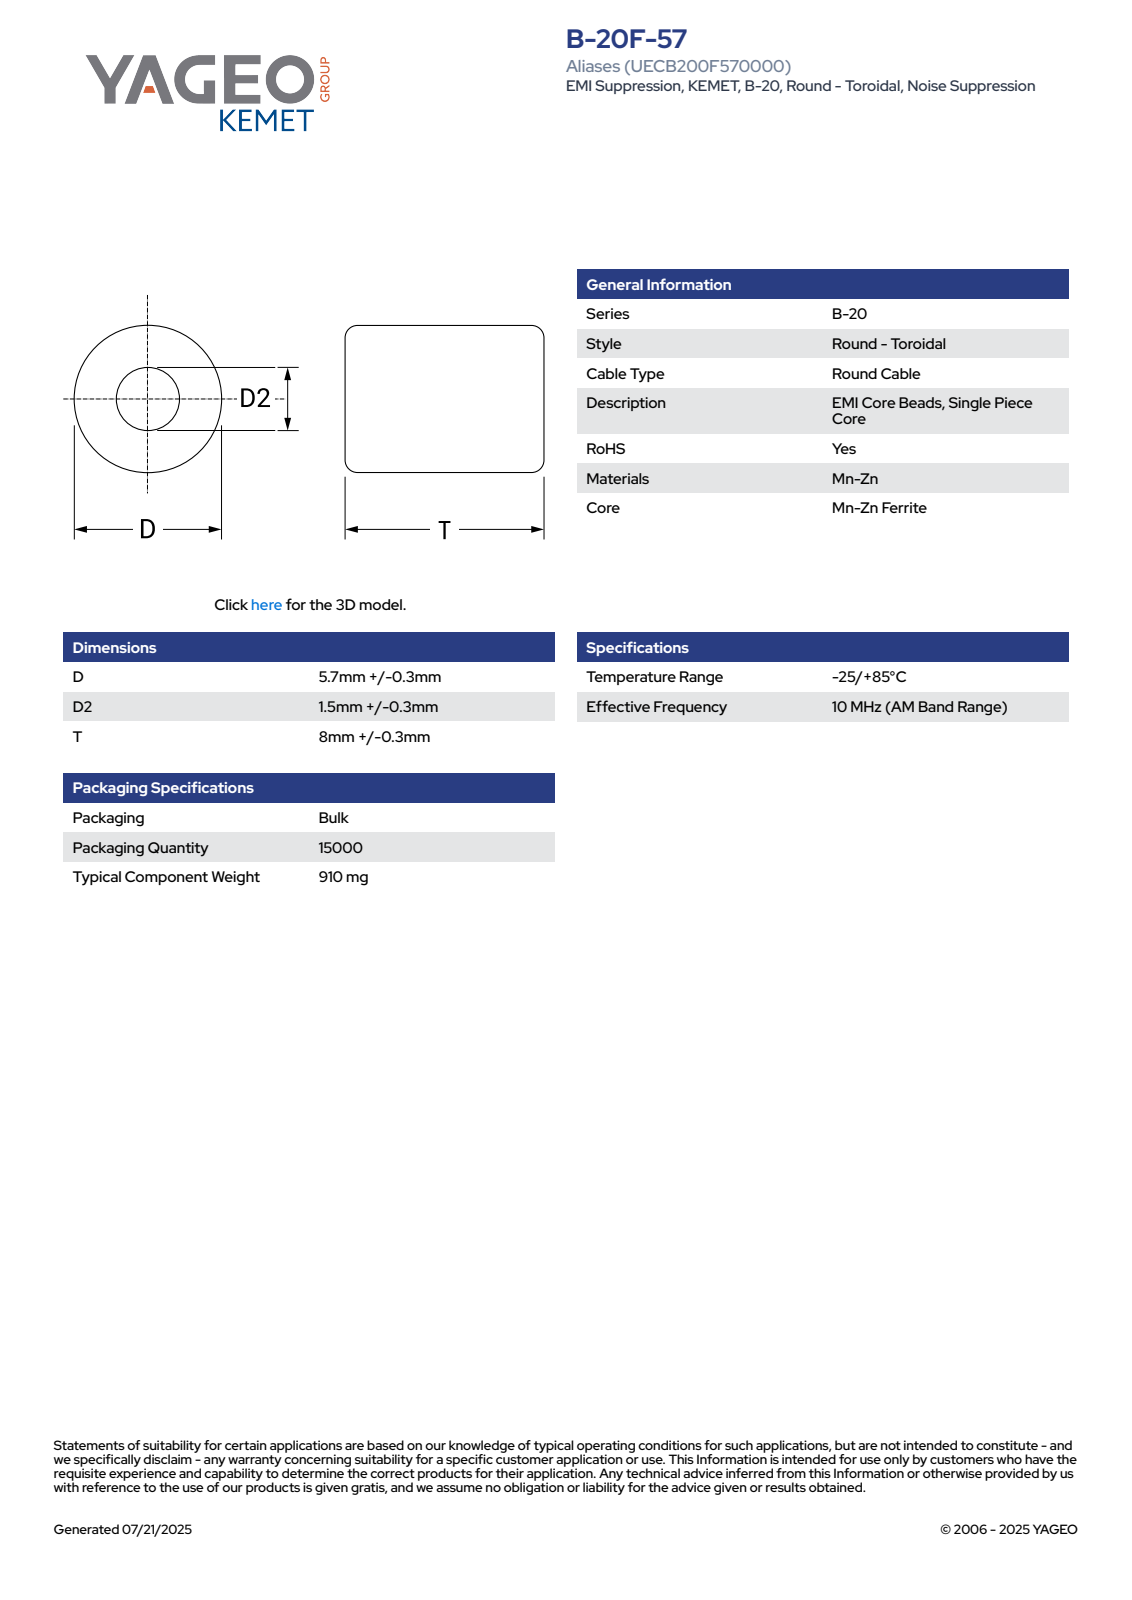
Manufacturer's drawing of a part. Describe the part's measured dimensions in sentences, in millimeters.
The part is named "EC_KBCH_D6D21.5T8.3". Its 3-D file was written by "SolidWorks 2021 (AUTOMOTIVE_DESIGN)". It is 1 solid with 66 faces: 25 planar, 7 cylindrical and 34 other. Overall it measures 8.3 by 6.01 by 6 millimeters. Its volume is 220 cubic millimeters and its surface area 246 square millimeters. Round holes: 1 of diameter 1.5. Round bosses or shafts: 1 of diameter 6. Partial cylindrical surfaces (rounded edges, fillets, slot ends): 1 of radius 3.01. The main face-to-face distances are 8.3, 3.96, 4.34, 0.38, 4.03, 4.27, 0.31, 4.2, 4.1, 4.13.
